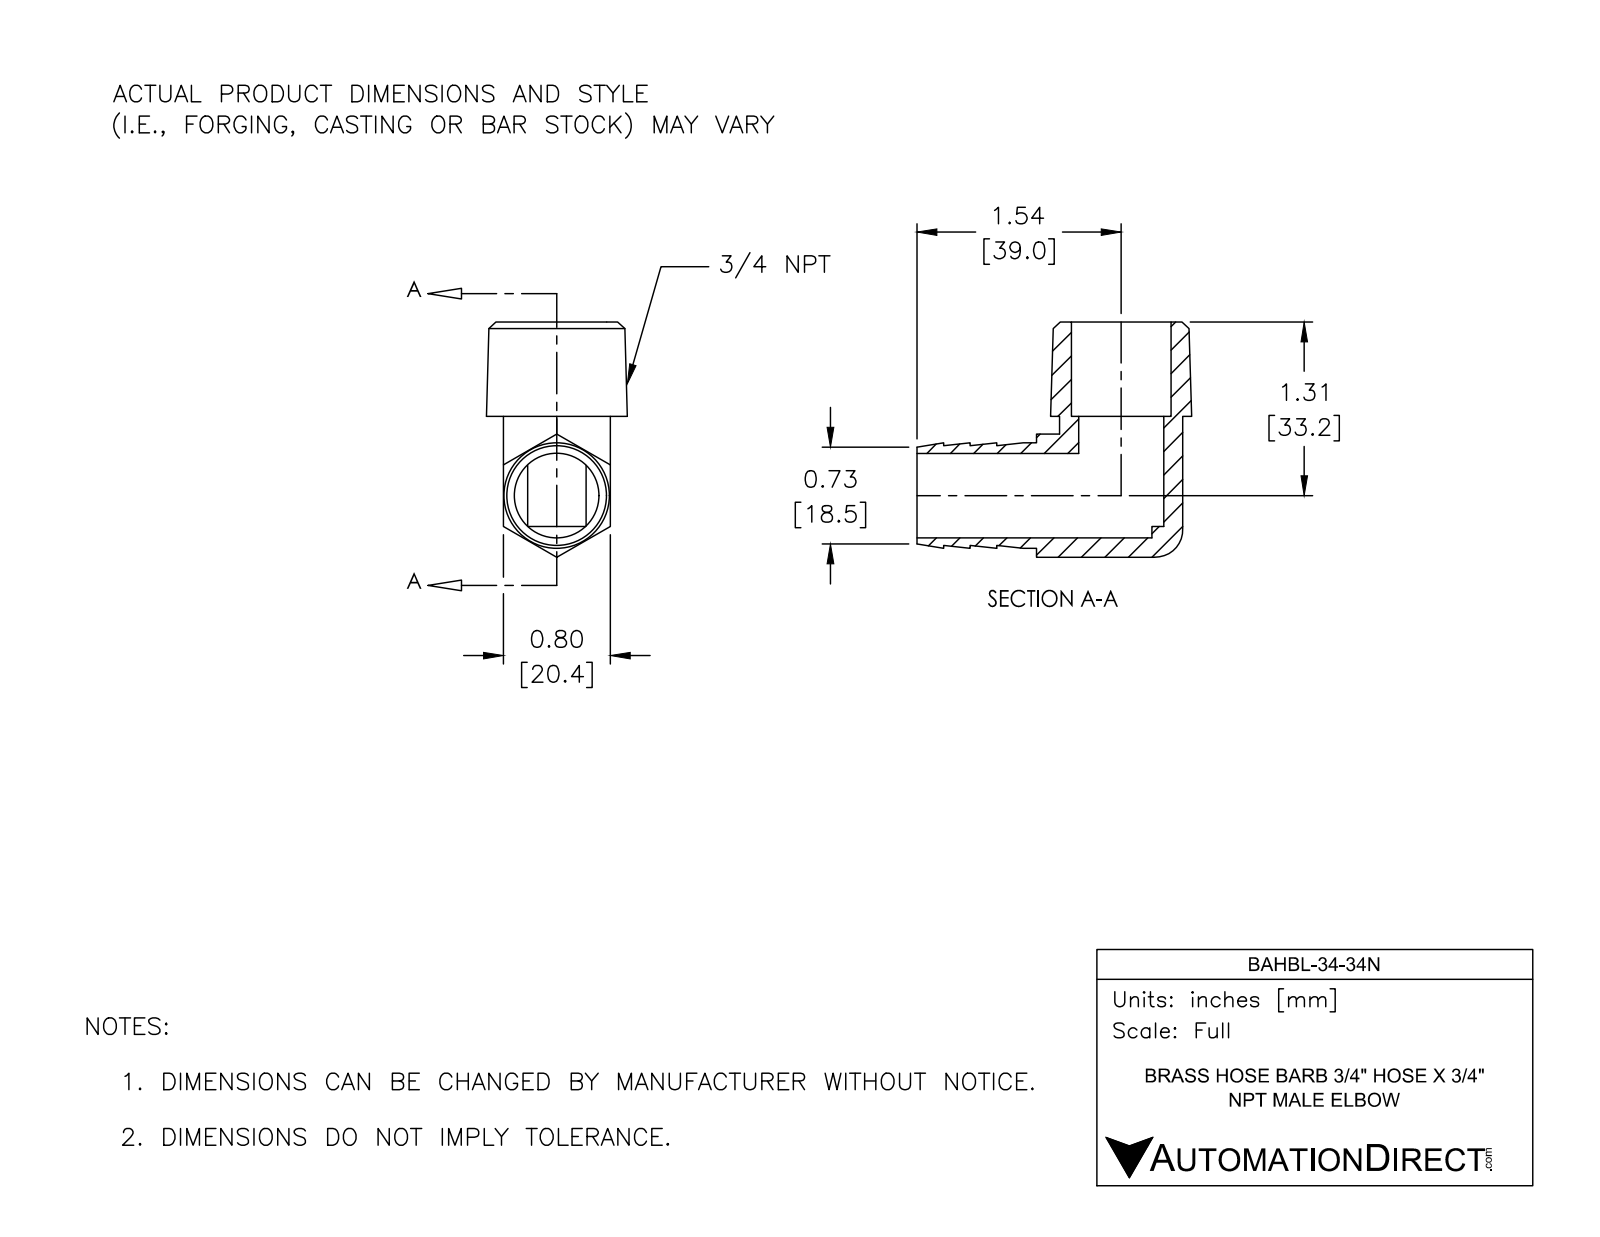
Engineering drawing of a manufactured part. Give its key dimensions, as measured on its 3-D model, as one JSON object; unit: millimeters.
{"part_name": "BAHBL-34-34N", "step_written_by": "SolidWorks 2017 (AUTOMOTIVE_DESIGN)", "units": "millimeters", "bodies": {"solids": 1, "faces": 47, "planar": 22, "cylindrical": 13, "other": 12}, "overall_size": [52.5, 45, 26.9], "volume_mm3": 11600, "surface_area_mm2": 9664, "round_holes": [[16.1, 1], [16.3, 1], [19.1, 1]], "round_bosses_or_shafts": [[20.2, 1]], "partial_cylinders_radius": [[6.4, 2]], "face_to_face_distances": [20.4, 18, 5.1, 10.2, 21, 39.1, 44.9, 22, 22.9, 29.7]}
